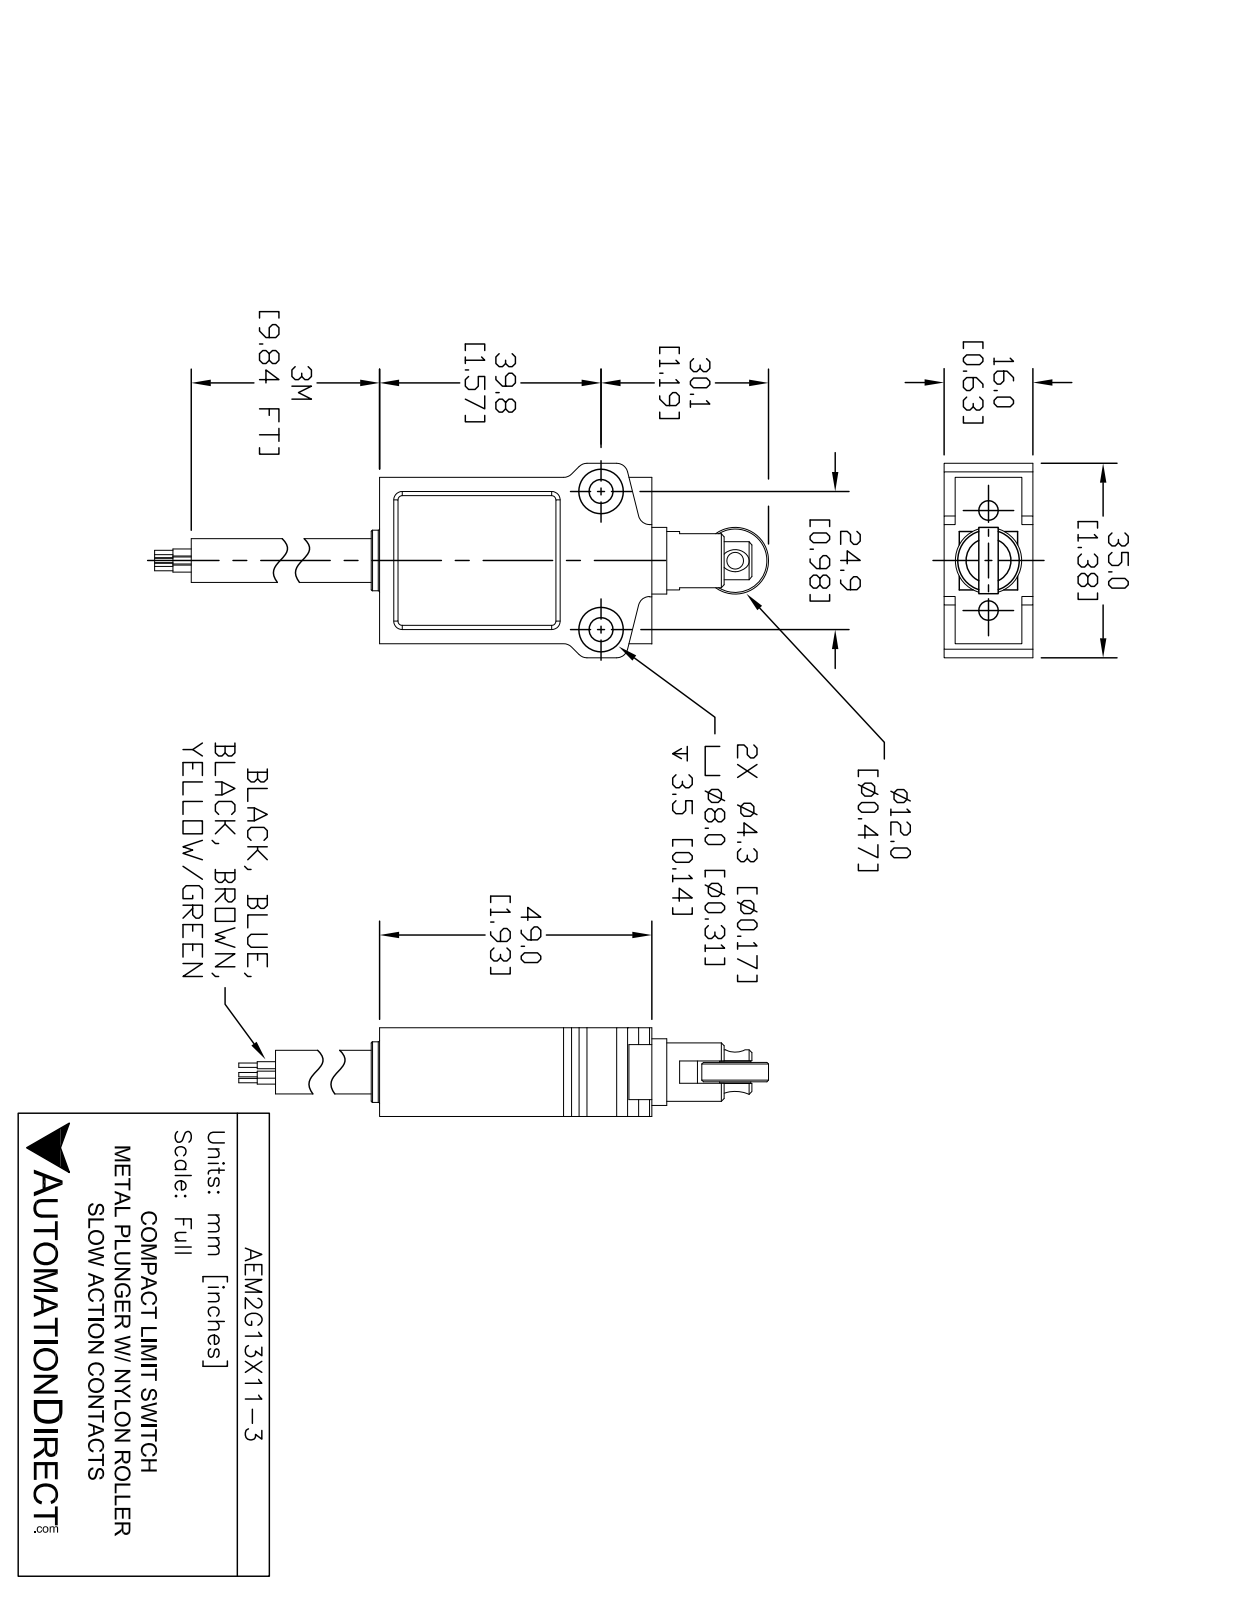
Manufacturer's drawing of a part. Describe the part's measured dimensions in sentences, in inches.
The part is named "AEM2G13X11-3_Default". Its 3-D file was written by "SolidWorks 2021 (CONFIG_CONTROL_DESIGN)". It is 2 solids with 116 faces: 53 planar, 43 cylindrical and 20 other. Overall it measures 3.375 by 1.38 by 0.63 inches. Its volume is 1.427 cubic inches and its surface area 11.97 square inches. Round holes: 2 of diameter 0.138, 2 of diameter 0.177, 2 of diameter 0.344. Round bosses or shafts: 5 of diameter 0.05, 5 of diameter 0.031, 2 of diameter 0.47, 1 of diameter 0.43, 1 of diameter 0.41, 1 of diameter 0.31. Partial cylindrical surfaces (rounded edges, fillets, slot ends): 8 of radius 0.03, 8 of radius 0.08, 1 of radius 0.135. The main face-to-face distances are 0.03, 0.6, 0.57, 0.63, 1.18, 1.93, 0.235, 0.395, 0.205, 0.365. The hole center spacings are 0.7, 0.98.
